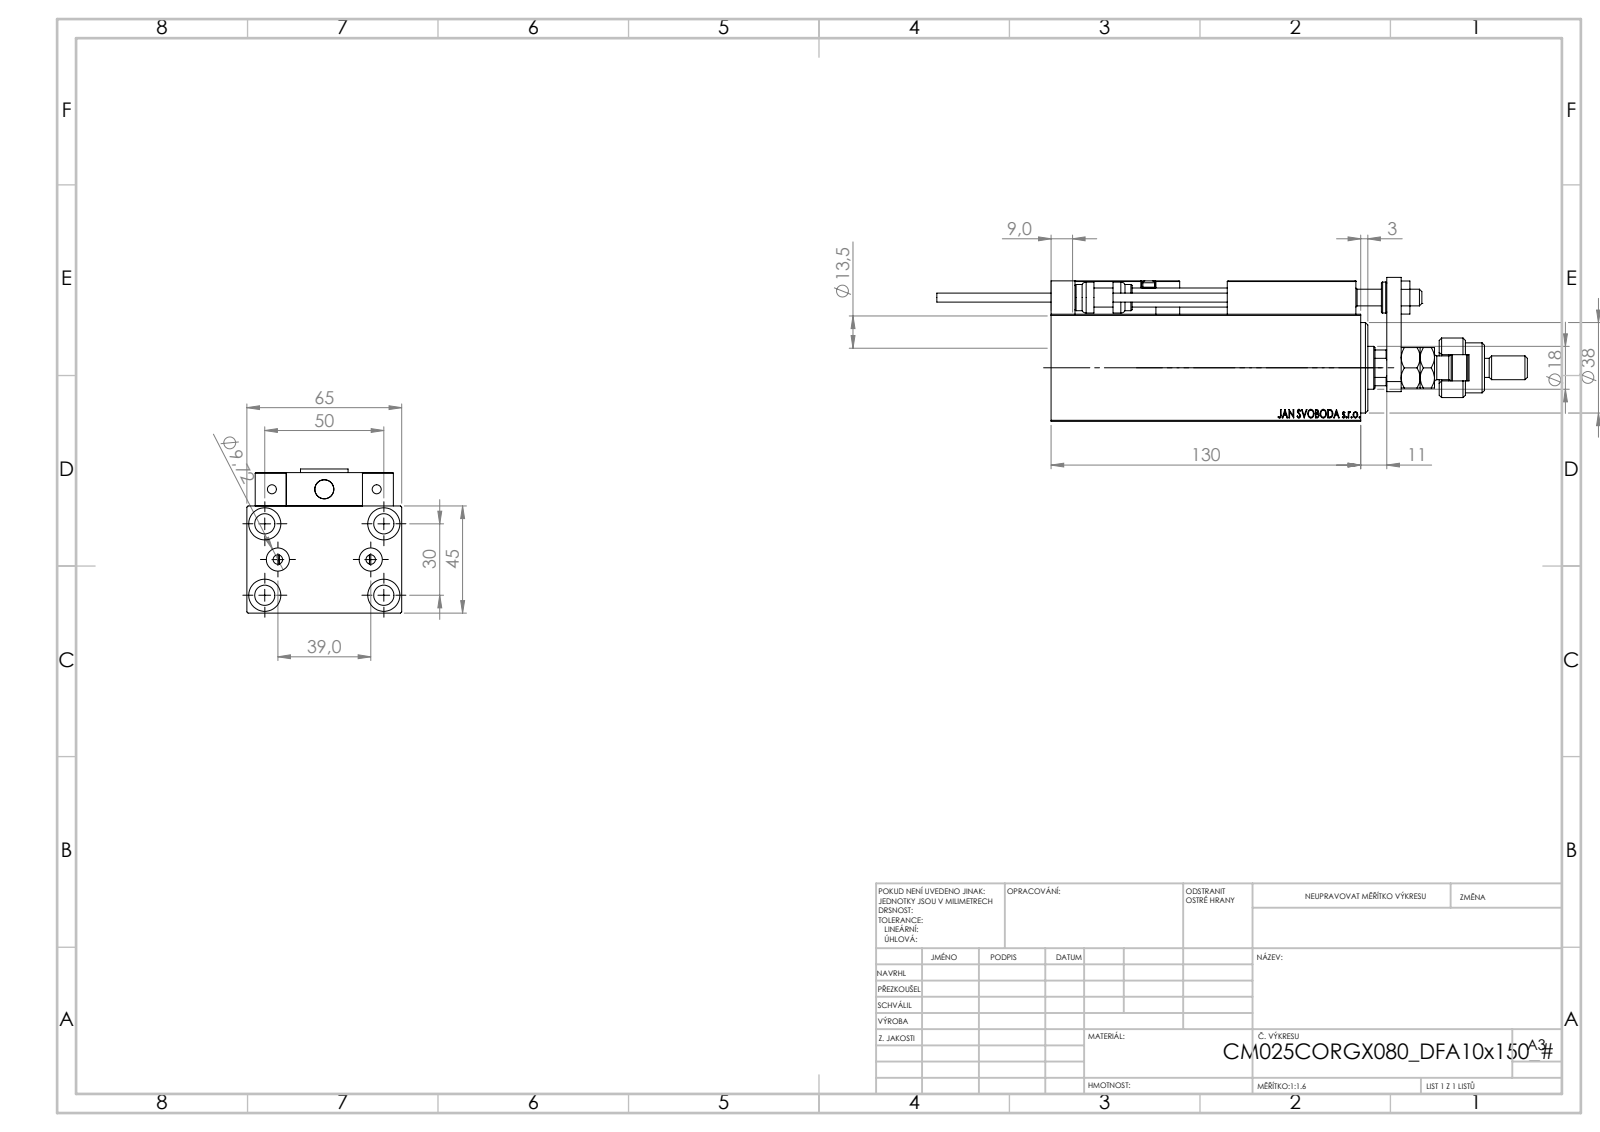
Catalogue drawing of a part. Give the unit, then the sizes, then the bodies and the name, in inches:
Units: inches
Overall size (bounding box): 9.764 × 2.559 × 2.382
Round holes (diameter × count): ⌀0.157 ×6, ⌀0.315 ×5, ⌀0.335 ×5, ⌀0.126 ×4, ⌀0.531 ×4, ⌀0.197 ×2, ⌀0.383 ×2, ⌀0.276 ×1, ⌀0.571 ×1, ⌀0.709 ×1, ⌀0.846 ×1, ⌀1.063 ×1
Round bosses / shafts (diameter × count): ⌀0.197 ×2, ⌀0.15 ×2, ⌀0.984 ×1, ⌀0.827 ×1, ⌀0.63 ×1, ⌀0.512 ×1, ⌀0.433 ×1, ⌀0.394 ×1
Partial cylindrical surfaces — rounded edges, fillets, slot ends (radius × count): R0.012 ×30, R0.118 ×2, R0.217 ×1, R0.335 ×1, R0.344 ×1
Main face-to-face distances: 1.772, 2.559, 0.551, 0.236, 2.323, 0.118, 0.276, 5.551, 0.748, 0.512
Hole centre spacings: 0.629, 1.148, 1.849, 0.448, 0.768, 0.787, 1.138, 1.165
Volume: 23.49 in³ · Surface area: 164.4 in²
Bodies: 25 solids, 1363 faces (588 planar, 197 cylindrical, 578 other)
Part name (STEP PRODUCT): ALLEN BOLT D5; MFA; TYC_L79; X_Y_DFA (+7 more)
STEP written by: SolidWorks 2019 (CONFIG_CONTROL_DESIGN)
